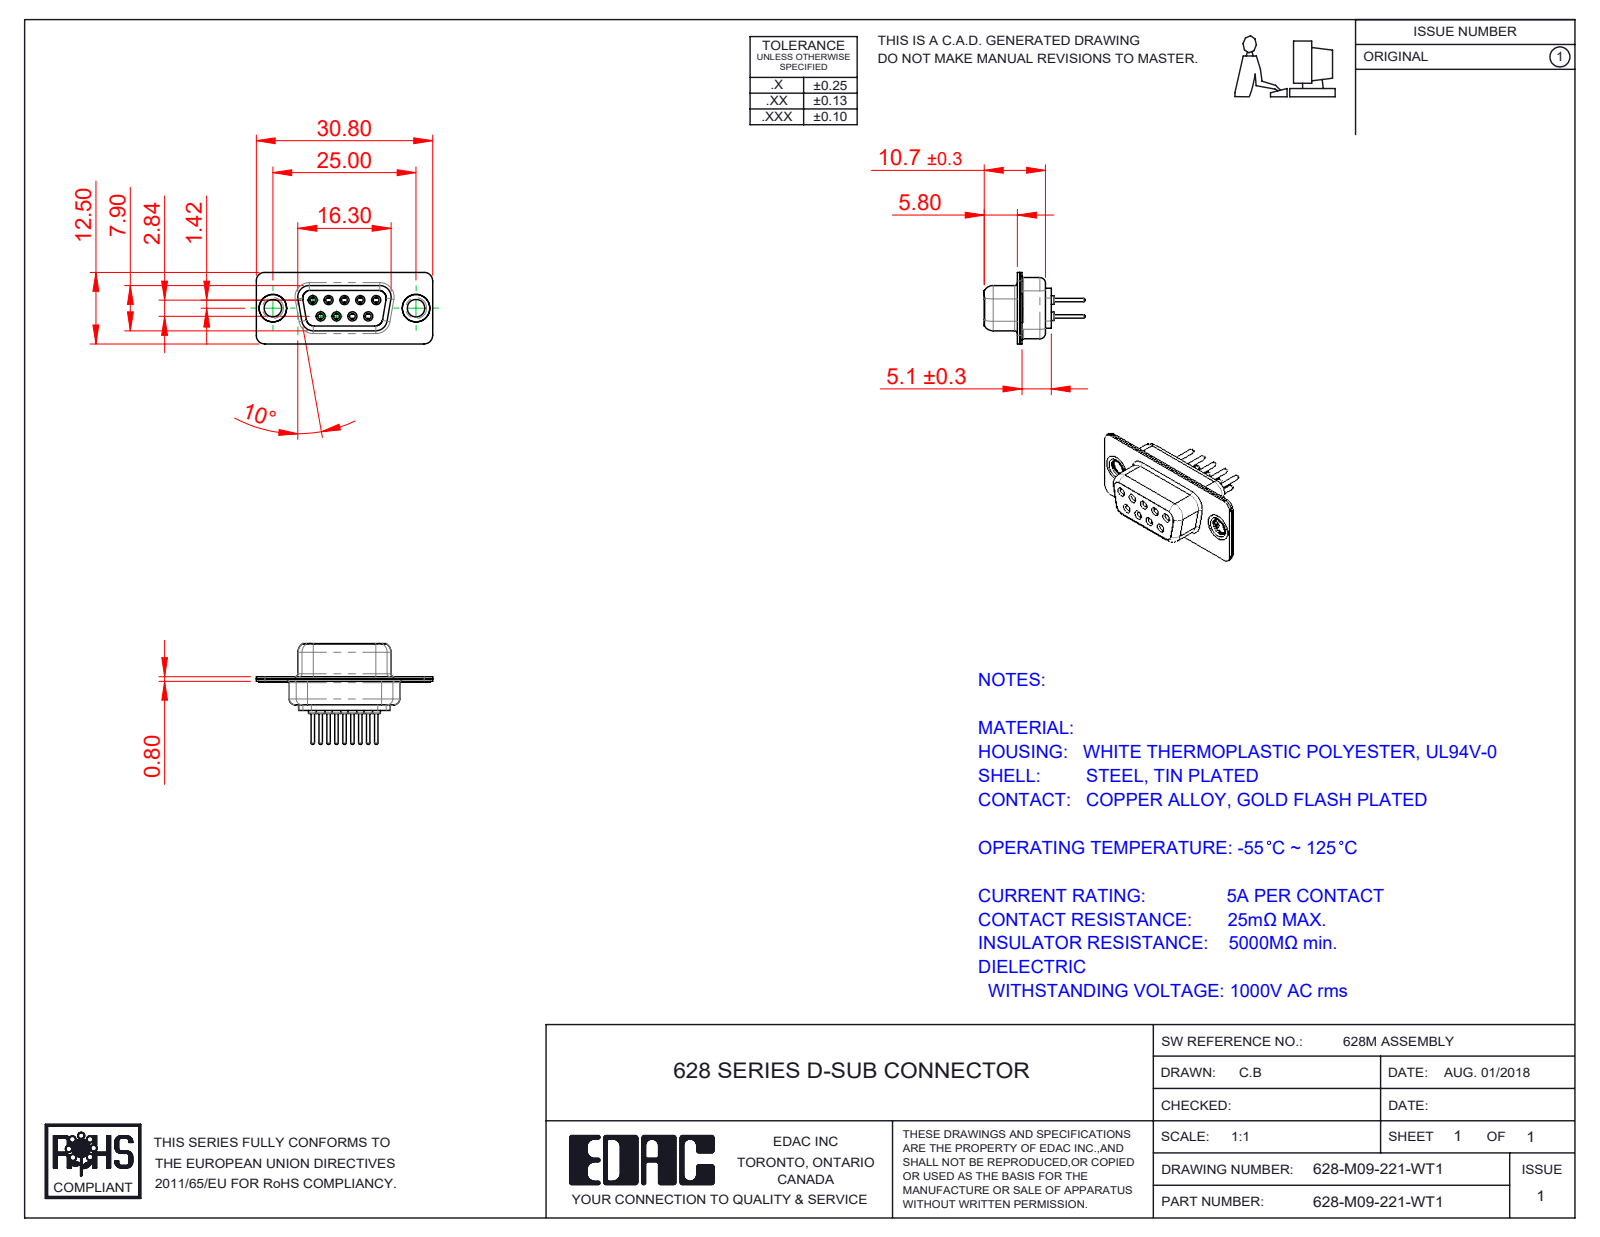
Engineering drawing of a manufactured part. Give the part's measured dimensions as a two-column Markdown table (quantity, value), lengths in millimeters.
| quantity | value |
| --- | --- |
| part name | 628M Shell Rear_09 Contacts; 628M Housing_09 Contacts; 628M Contact Row 1_21; 628-M09-221-WT1 (+3 more) |
| STEP written by | SolidWorks 2020 (CONFIG_CONTROL_DESIGN) |
| units | millimeters |
| bodies | 14 solids, 748 faces (202 planar, 292 cylindrical, 254 other) |
| overall size | 30.8 × 17.6 × 12.5 |
| volume | 1 624 mm³ |
| surface area | 4 277 mm² |
| round holes (diameter × count) | 1 × 9, 1.1 × 9, 1.7 × 9, 1.8 × 9, 2 × 9, 3.05 × 2, 4 × 2, 4.8 × 2 |
| round bosses / shafts (diameter × count) | 2.2 × 9, 1.6 × 9, 1.5 × 9, 0.6 × 9, 5 × 2, 4.9 × 2, 3.55 × 2 |
| partial cylindrical surfaces (radius × count) | 1.5 × 16, 2 × 12, 1.35 × 8, 1.6 × 8, 0.25 × 4, 0.5 × 4, 0.6 × 4, 0.65 × 4 |
| main face-to-face distances | 0.4, 1.4, 0.45, 8.45, 0.8, 8.9, 1.8, 1, 6.2, 1.35 |
| hole center spacings | 3.16, 2.77, 5.54, 5.03, 5.04, 8.31, 7.1, 7.48 |
